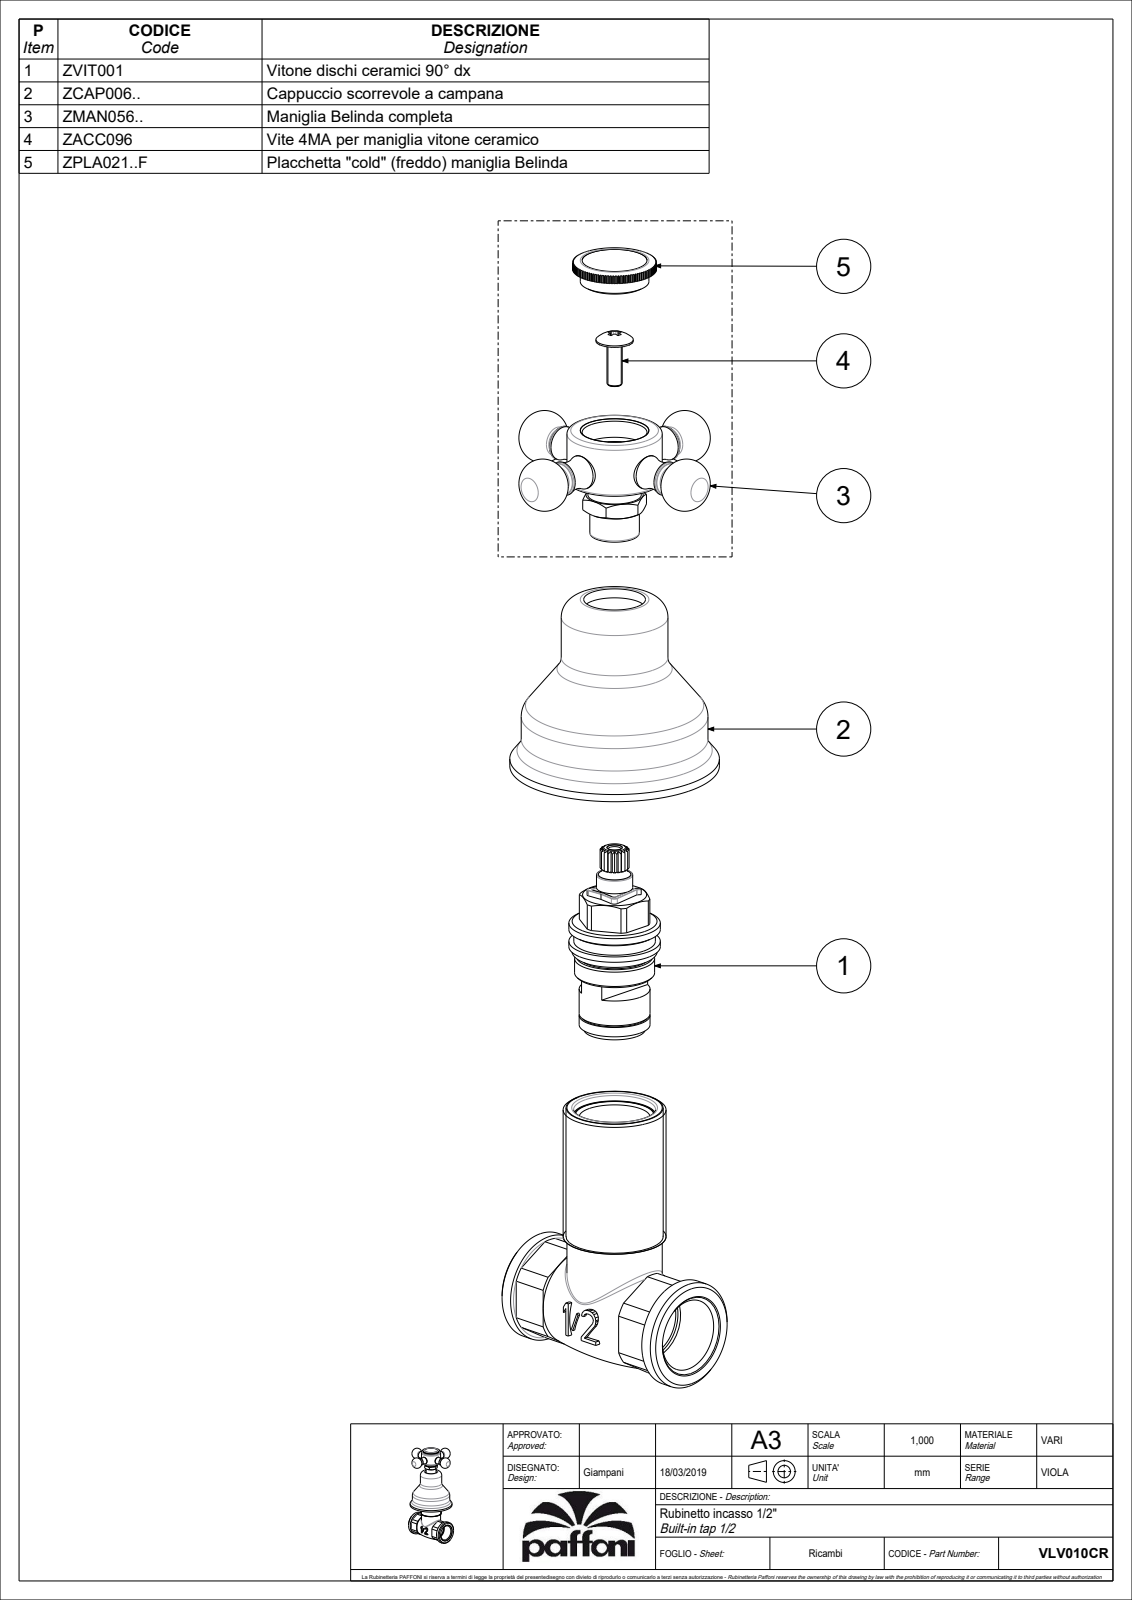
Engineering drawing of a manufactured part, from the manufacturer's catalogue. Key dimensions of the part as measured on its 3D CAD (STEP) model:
Part name (STEP PRODUCT): VLV010CR
STEP written by: CREO PARAMETRIC BY PTC INC, 2020044 (CONFIG_CONTROL_DESIGN)
Units: millimetres
Bodies: 1 solid, 435 faces (217 planar, 138 cylindrical, 80 other)
Overall size (bounding box): 76.4 × 64.07 × 64.07
Volume: 73 617 mm³ · Surface area: 14 347 mm²
Round bosses / shafts (diameter × count): ⌀9 ×2, ⌀7 ×2, ⌀55 ×1, ⌀49 ×1, ⌀28 ×1, ⌀25 ×1, ⌀14 ×1, ⌀13 ×1
Partial cylindrical surfaces — rounded edges, fillets, slot ends (radius × count): R11 ×1
Main face-to-face distances: 59.7, 46.5, 13.2, 15, 15.2, 4, 51.7, 5.2, 8, 73.7
